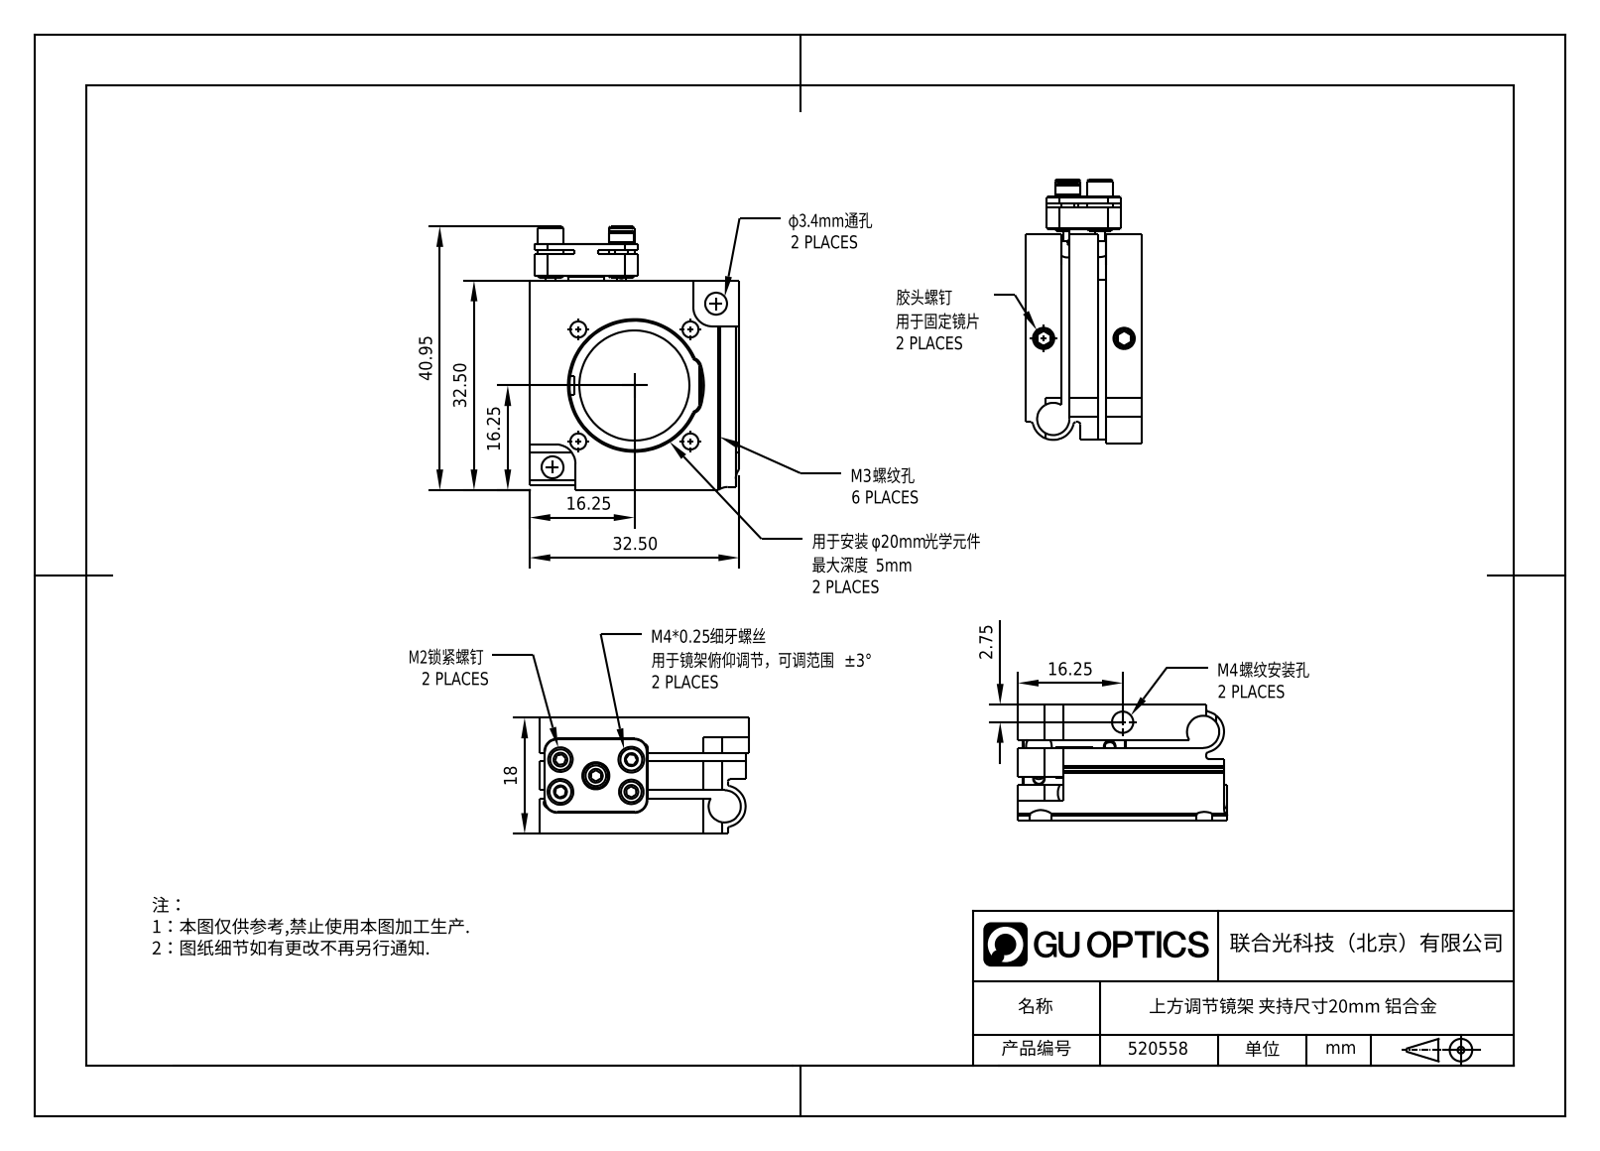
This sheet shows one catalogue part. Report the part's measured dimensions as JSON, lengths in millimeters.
{"part_name": "耳1.5 440C粣創詩埴翐种_33.2.25-DZ-耳1.5*5; 1.1.6.46-ZJR-S20; 30.1.圆柱头内六角不锈钢螺丝_30.1.18-M2*6; 1.1.6.1.4_标准挠性光学调整架调节块顶杆，零部件 (+3 more)", "step_written_by": "SolidWorks 2021 (CONFIG_CONTROL_DESIGN)", "units": "millimeters", "bodies": {"solids": 17, "faces": 474, "planar": 173, "cylindrical": 170, "other": 131}, "overall_size": [40.95, 32.5, 18], "volume_mm3": 9878, "surface_area_mm2": 10165, "round_holes": [[2.5, 6], [3.3, 5], [1.5, 3], [1.6, 3], [2.1, 2], [3.4, 2], [5, 2], [2.2, 1], [4, 1], [17.1, 1], [20.1, 1]], "round_bosses_or_shafts": [[1.5, 5], [4, 4], [3.8, 3], [2, 3], [3, 2]], "partial_cylinders_radius": [[0.35, 6], [2, 6], [1.5, 4], [0.75, 3], [0.5, 2], [2.25, 2], [2.5, 2], [3, 2]], "face_to_face_distances": [5.75, 11.25, 6.75, 1.25, 12.5, 5.5, 4.5, 7, 18, 0.5], "hole_center_spacings": [21.77, 5.66, 6.04, 12.3, 17.4, 17.96, 25.4, 30.26]}
